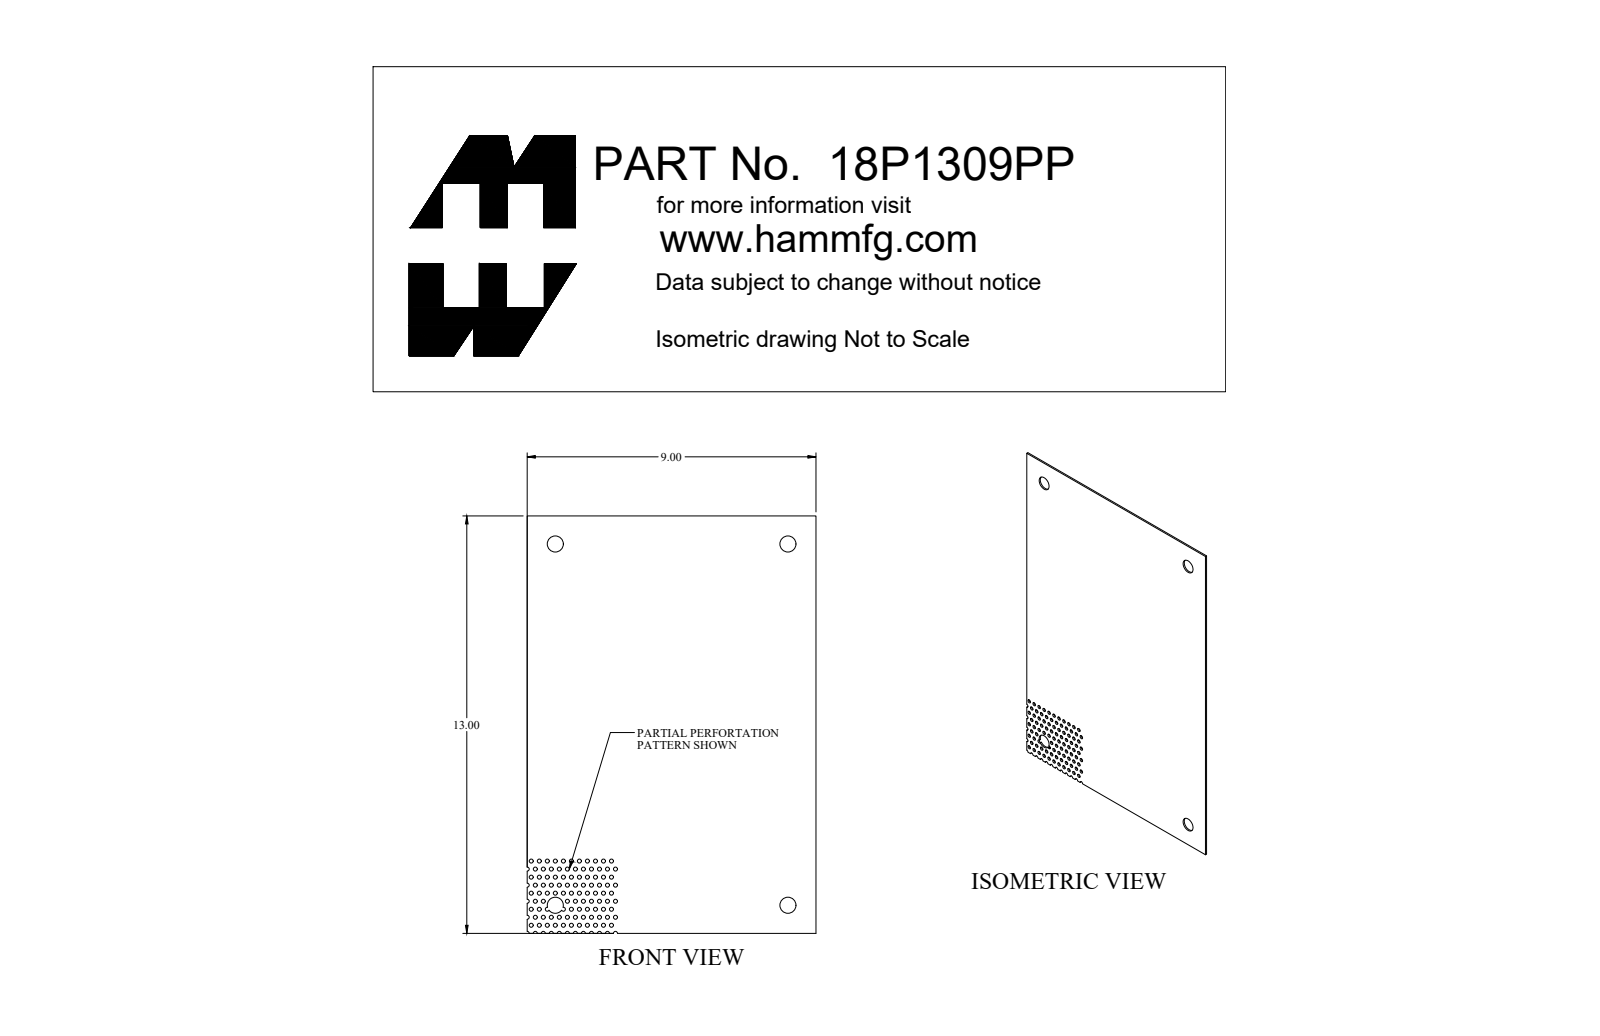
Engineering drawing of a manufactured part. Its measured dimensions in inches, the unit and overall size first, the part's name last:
Units: inches
Overall size (bounding box): 13 × 9 × 0.057
Round holes (diameter × count): ⌀0.125 ×61, ⌀0.125 ×33, ⌀0.5 ×4
Partial cylindrical surfaces — rounded edges, fillets, slot ends (radius × count): R0.062 ×17, R0.063 ×1
Main face-to-face distances: 0.057, 9, 13
Hole centre spacings: 0.28, 0.5, 0.25, 0.45, 0.451, 0.673, 0.673, 0.75
Volume: 6.552 in³ · Surface area: 234.9 in²
Bodies: 1 solid, 251 faces (21 planar, 230 cylindrical, 0 other)
Part name (STEP PRODUCT): 18P1309PP_Default
STEP written by: SolidWorks 2018 (CONFIG_CONTROL_DESIGN)
